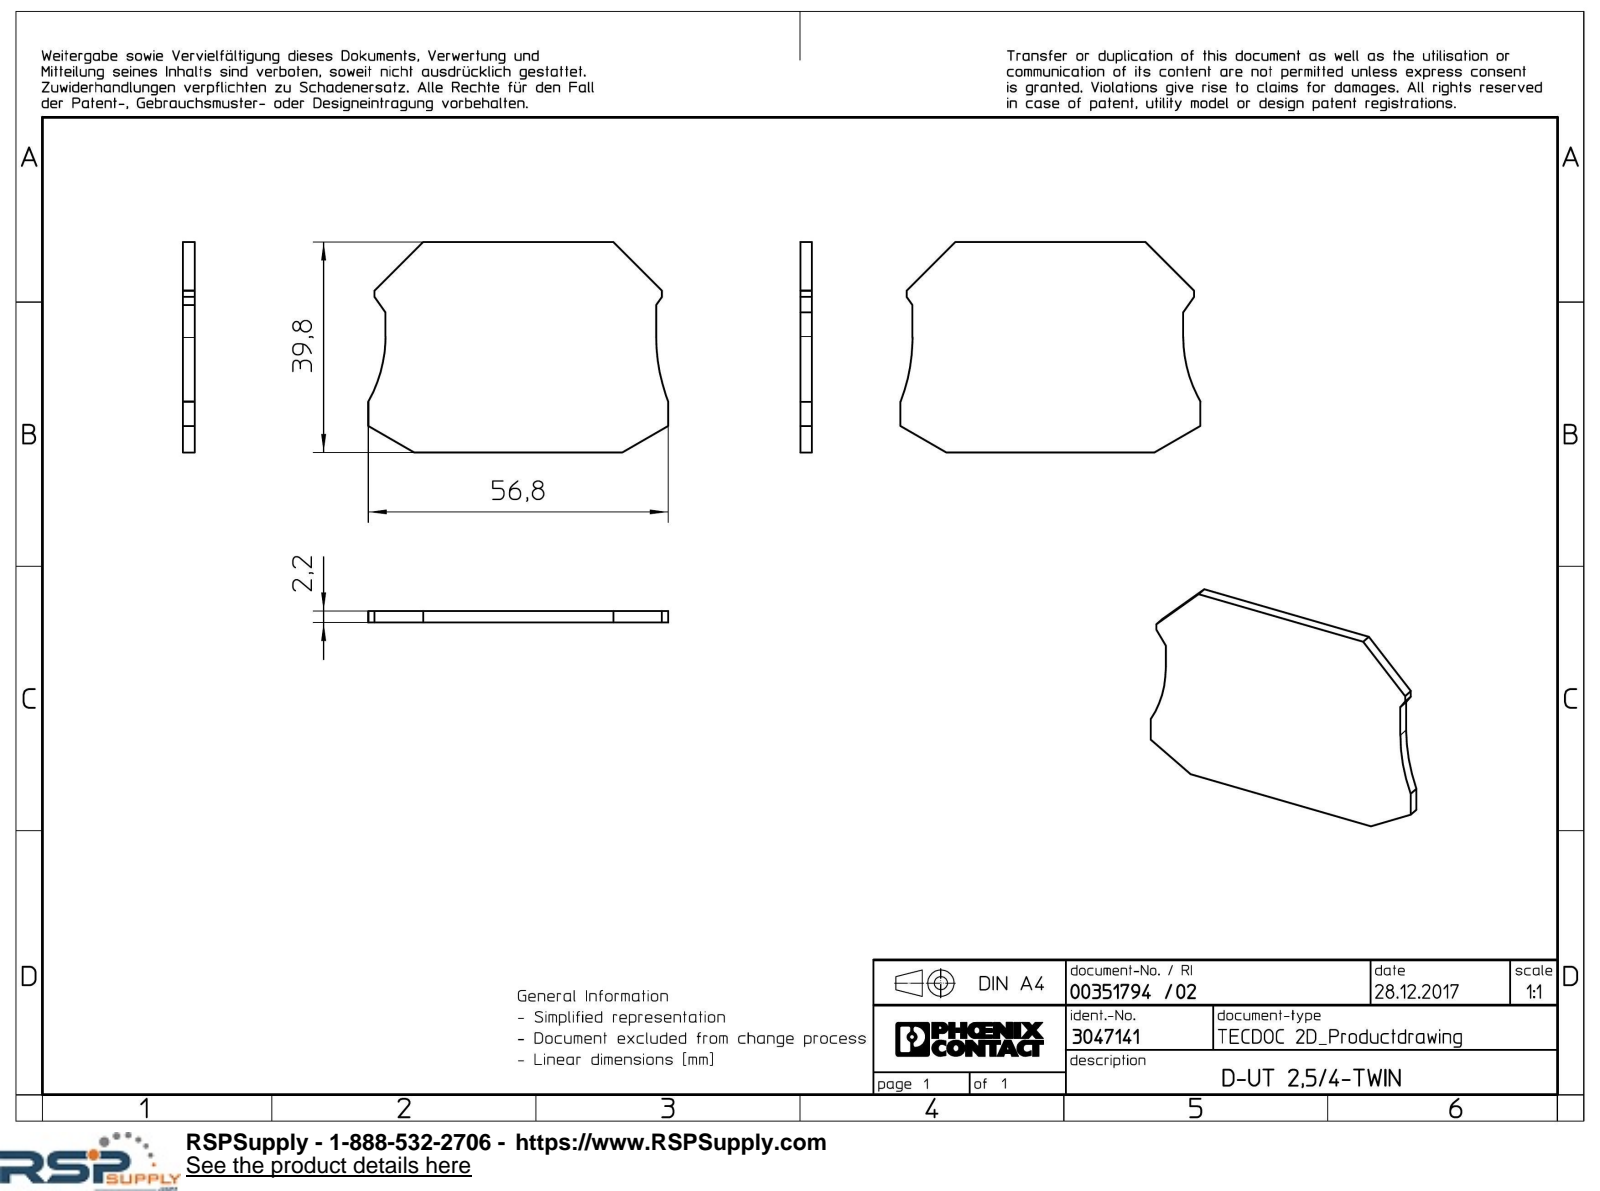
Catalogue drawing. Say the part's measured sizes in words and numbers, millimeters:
The part is named "D_UT_2.5_4_TWIN-select". Its 3-D file was written by "Creo Elements/Direct Modeling 18.1I 14-Aug-2016 (C) Parametric Technology GmbH (AUTOMOTIVE_DESIGN)". It is 1 solid with 18 faces: 16 planar, 2 cylindrical and 0 other. Overall it measures 56.8 by 39.8 by 2.2 millimeters. Its volume is 4 454 cubic millimeters and its surface area 4 433 square millimeters. Partial cylindrical surfaces (rounded edges, fillets, slot ends): 1 of radius 25, 1 of radius 34. The main face-to-face distances are 2.2, 39.8, 2.25, 51.3, 53.55, 3.25, 54.55, 56.8, 1.2, 55.6.
